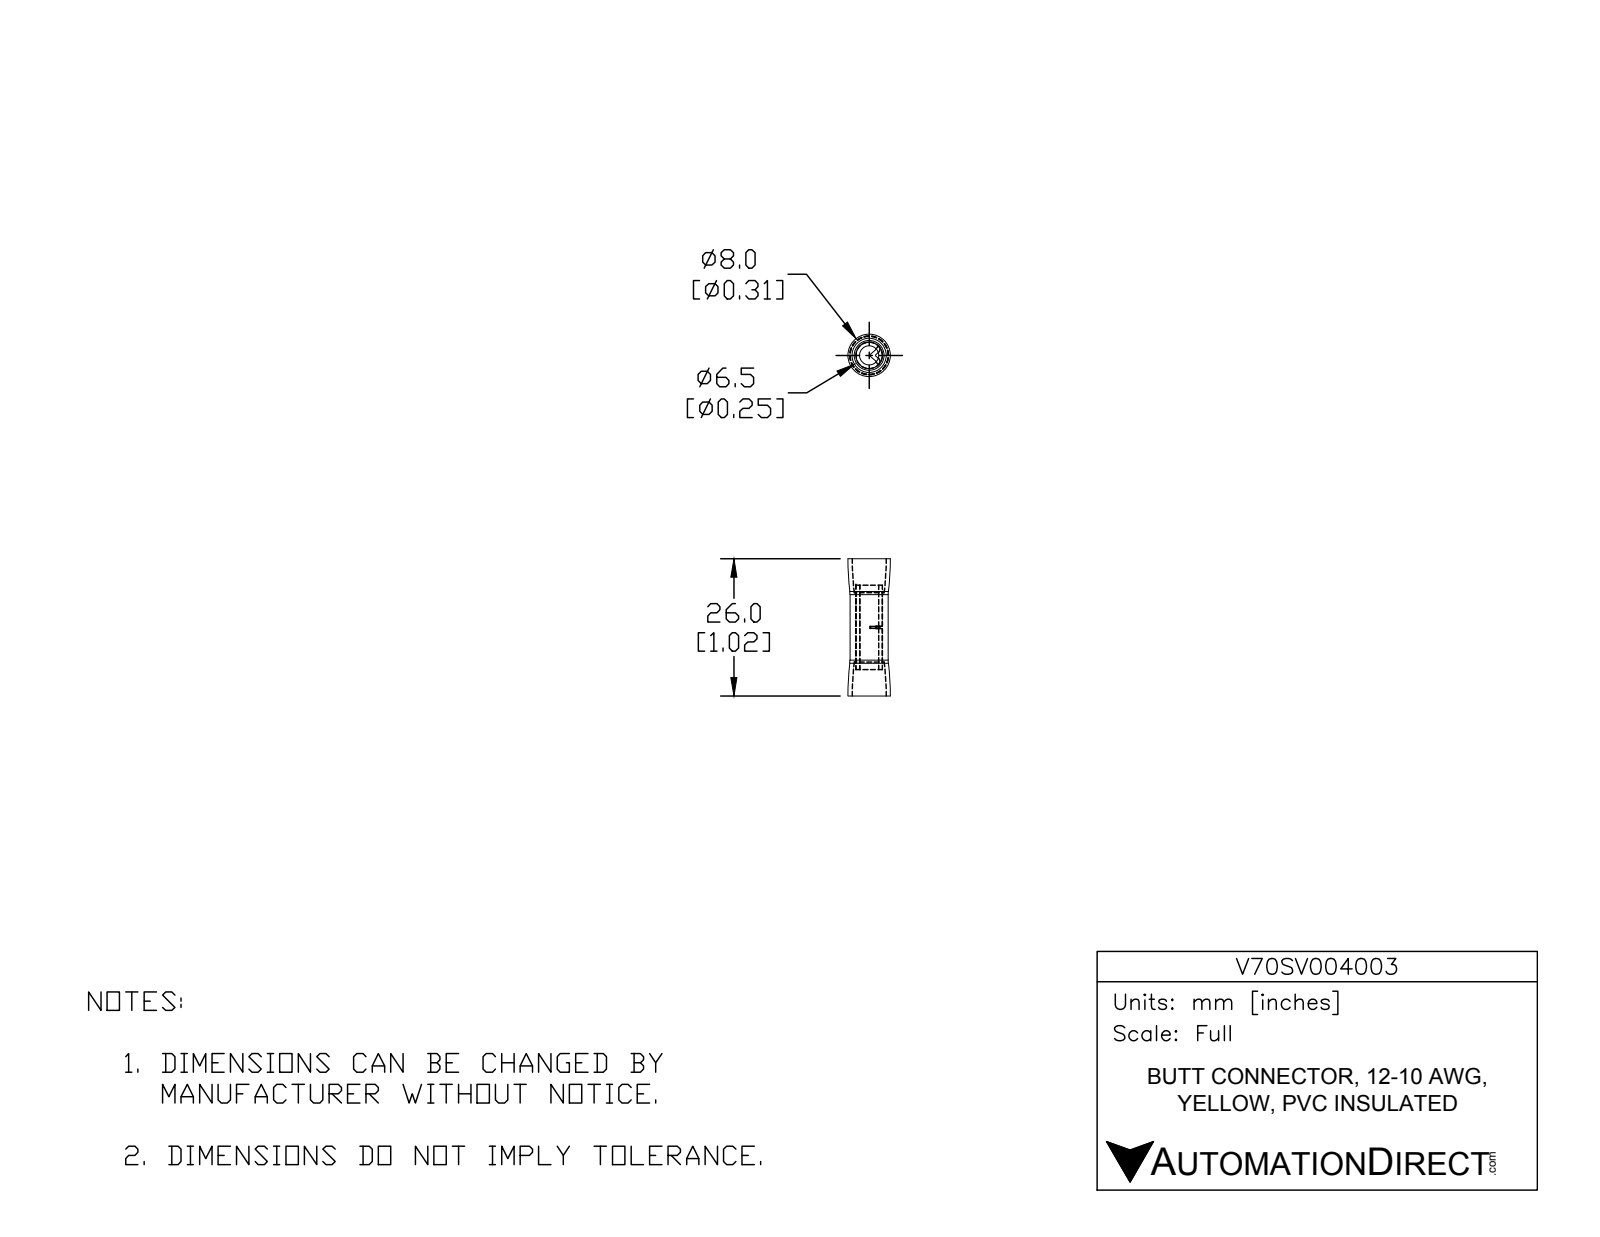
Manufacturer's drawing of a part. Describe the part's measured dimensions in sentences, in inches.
The part is named "V70SV004003". Its 3-D file was written by "SolidWorks 2017 (AUTOMOTIVE_DESIGN)". It is 2 solids with 45 faces: 20 planar, 13 cylindrical and 12 other. Overall it measures 1.024 by 0.315 by 0.315 inches. Its volume is 0.039 cubic inches and its surface area 2.475 square inches. Round holes: 1 of diameter 0.142, 1 of diameter 0.197. Round bosses or shafts: 1 of diameter 0.283. Partial cylindrical surfaces (rounded edges, fillets, slot ends): 2 of radius 0.006, 2 of radius 0.01, 2 of radius 0.033. The main face-to-face distances are 0.197, 0.827, 1.024, 0.254, 0.77, 0.057, 0.573, 0.63, 0.504, 0.52.
